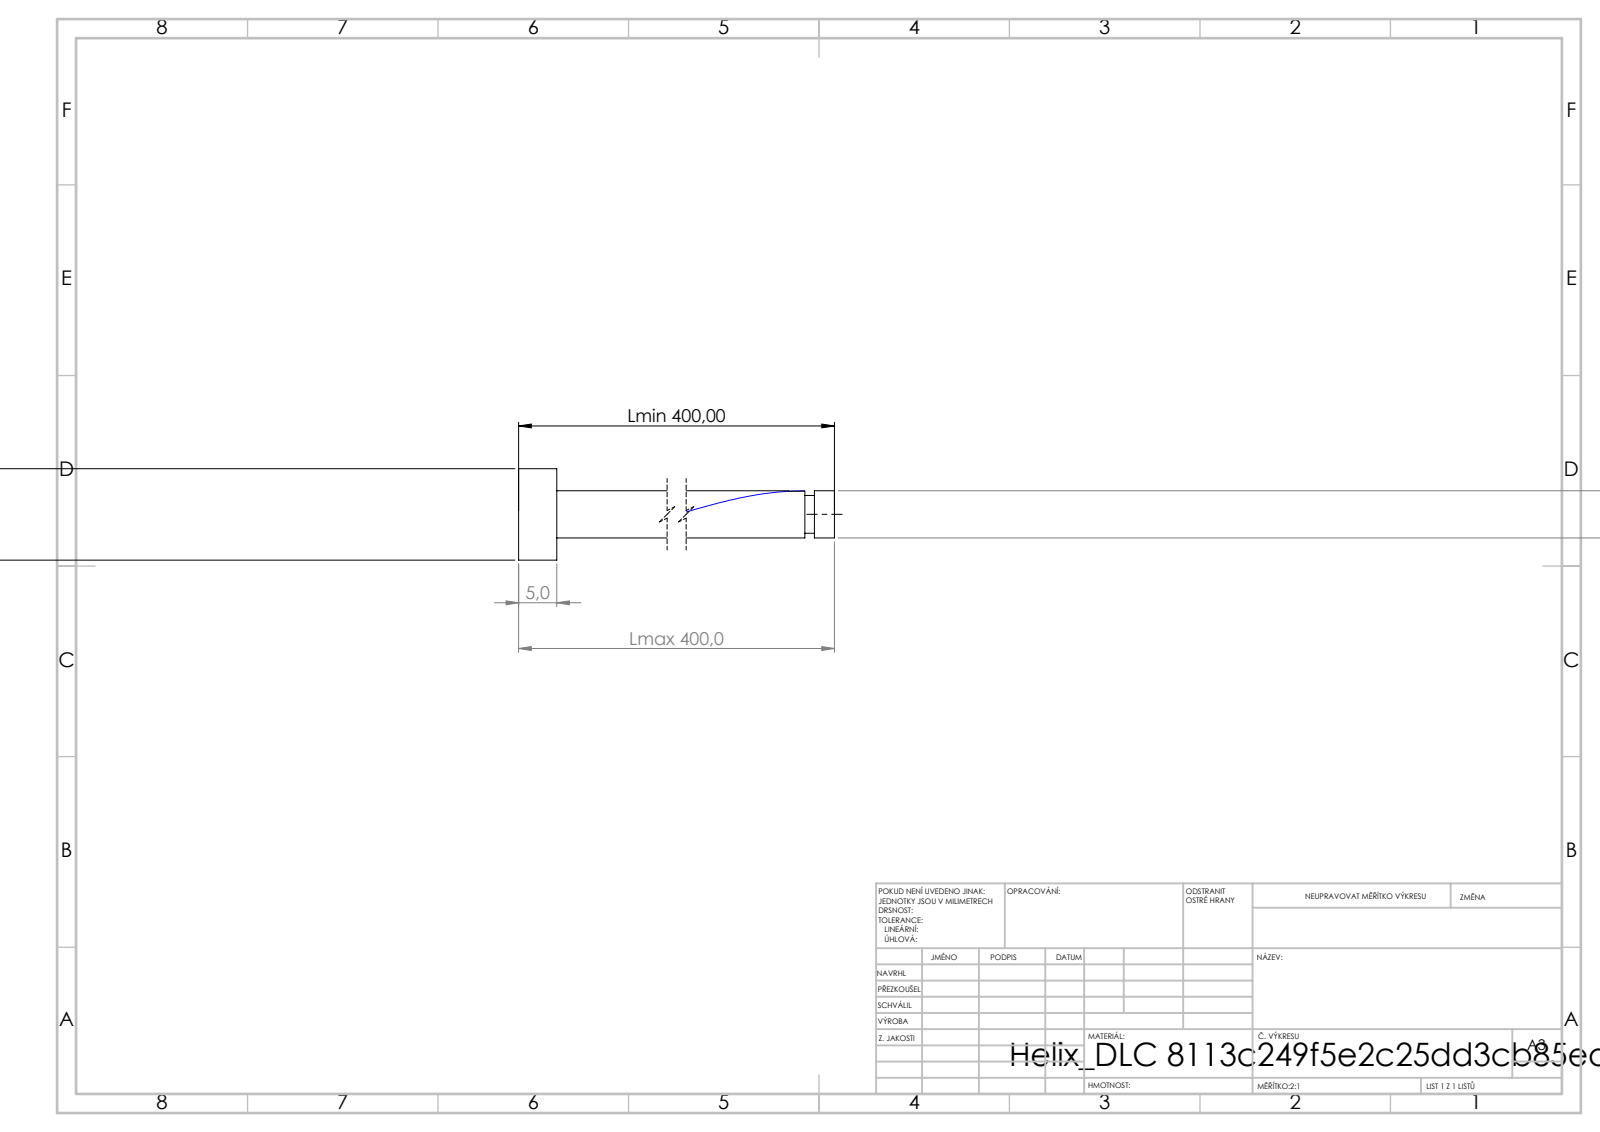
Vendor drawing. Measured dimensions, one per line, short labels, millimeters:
written by: SolidWorks 2019 (CONFIG_CONTROL_DESIGN)
unit: mm
bodies: 1 solid, 16 faces (6 planar, 9 cylindrical, 1 other)
size: 400 × 12 × 12
volume: 15 047 mm³; area: 10 847 mm²
bosses: 1× ⌀12, 1× ⌀6.2, 1× ⌀4.96
face distances: 5, 400, 395, 397.36, 392.36, 2.64, 396.12, 391.12, 1.24, 3.88
